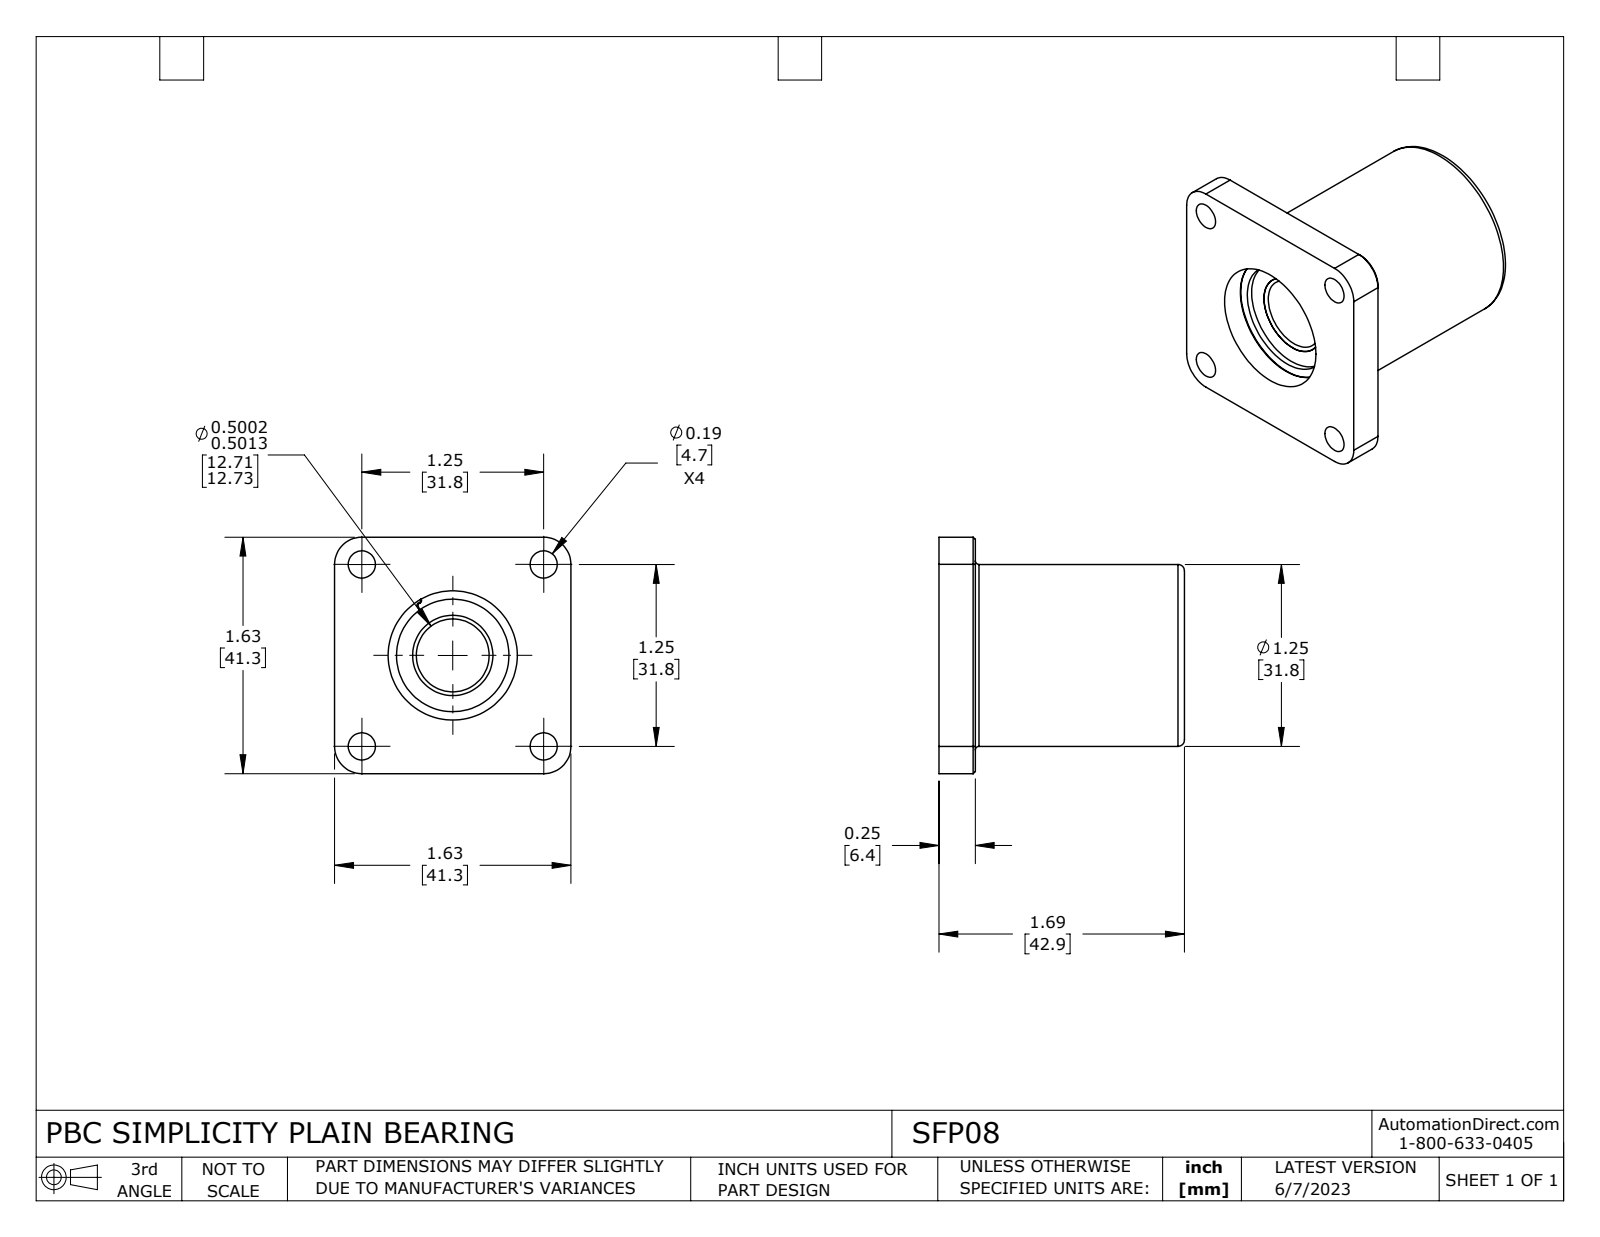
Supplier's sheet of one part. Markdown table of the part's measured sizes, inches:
| quantity | value |
| --- | --- |
| part name | SFP08 |
| STEP written by | SolidWorks 2021 (CONFIG_CONTROL_DESIGN) |
| units | inches |
| bodies | 7 solids, 169 faces (41 planar, 74 cylindrical, 54 other) |
| overall size | 1.688 × 1.625 × 1.625 |
| volume | 1.845 in³ |
| surface area | 30.54 in² |
| round holes (diameter × count) | 0.187 × 4, 0.501 × 1, 0.552 × 1, 0.773 × 1, 0.888 × 1, 0.931 × 1 |
| round bosses / shafts (diameter × count) | 1.25 × 1, 0.943 × 1, 0.874 × 1, 0.82 × 1, 0.712 × 1 |
| partial cylindrical surfaces (radius × count) | 0.014 × 4, 0.187 × 4, 0.009 × 2, 0.019 × 2 |
| main face-to-face distances | 0.25, 1.625, 0.164, 1.524, 1.688, 1.438, 0.37, 0.495, 0.748, 0.873 |
| hole center spacings | 0.884, 1.25, 1.769 |
